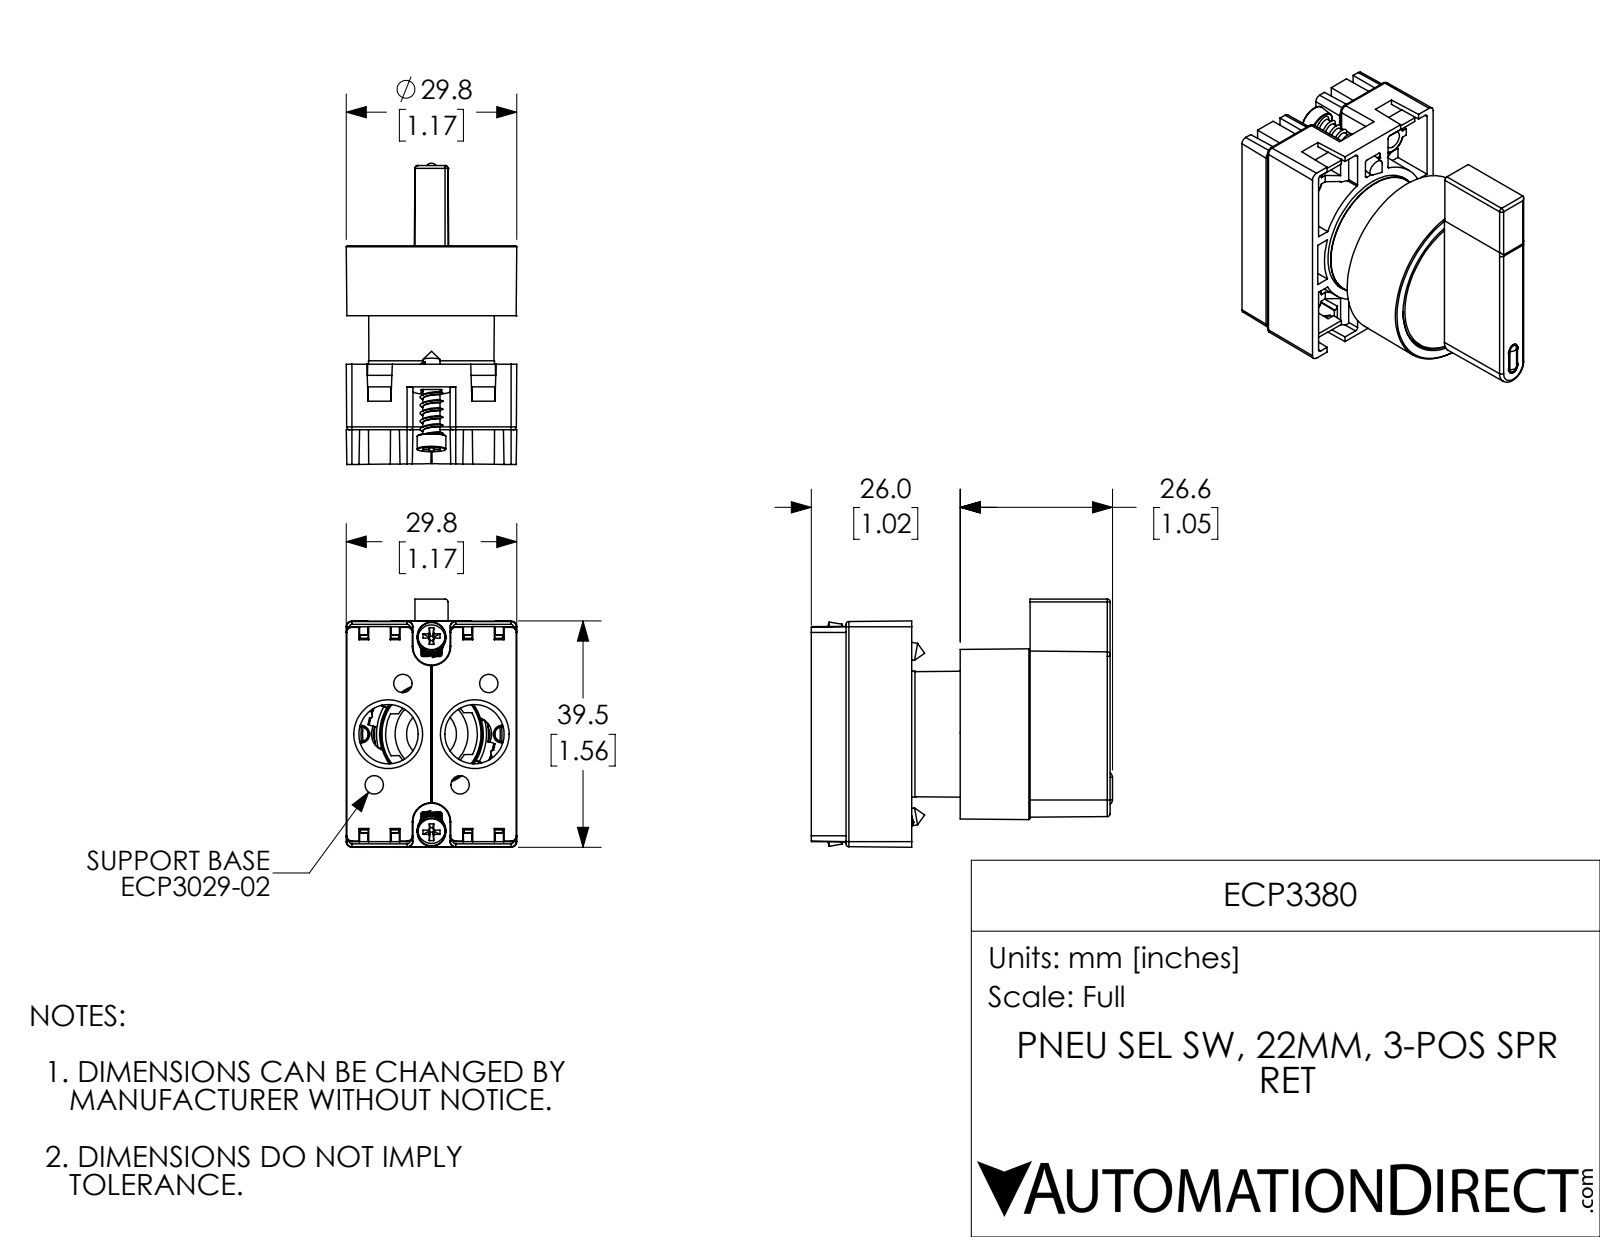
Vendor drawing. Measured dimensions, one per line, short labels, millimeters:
name: ECP3380
written by: SolidWorks 2017 (AUTOMOTIVE_DESIGN)
unit: mm
bodies: 9 solids, 850 faces (410 planar, 161 cylindrical, 279 other)
size: 52.6 × 43.3 × 29.8
volume: 18 750 mm³; area: 20 890 mm²
holes: 4× ⌀2.1, 2× ⌀10.3, 1× ⌀12.7, 1× ⌀14, 1× ⌀17.7, 1× ⌀19.1, 1× ⌀19.2, 1× ⌀21.7, 1× ⌀24.8, 1× ⌀26
bosses: 2× ⌀5, 2× ⌀3, 1× ⌀25.5, 1× ⌀22, 1× ⌀21.6, 1× ⌀17, 1× ⌀8.7
rounds: 23× R0.5, 10× R0.3, 9× R1, 8× R0.2, 4× R0.2, 2× R0.2, 2× R3, 2× R3.3
face distances: 32.1, 1.5, 1.7, 18.1, 18.9, 7.6, 18.1, 18.2, 20.7, 11.5
hole spacings: 7.7, 13.7, 20.8, 7.5, 12, 24.7, 27.5, 15
